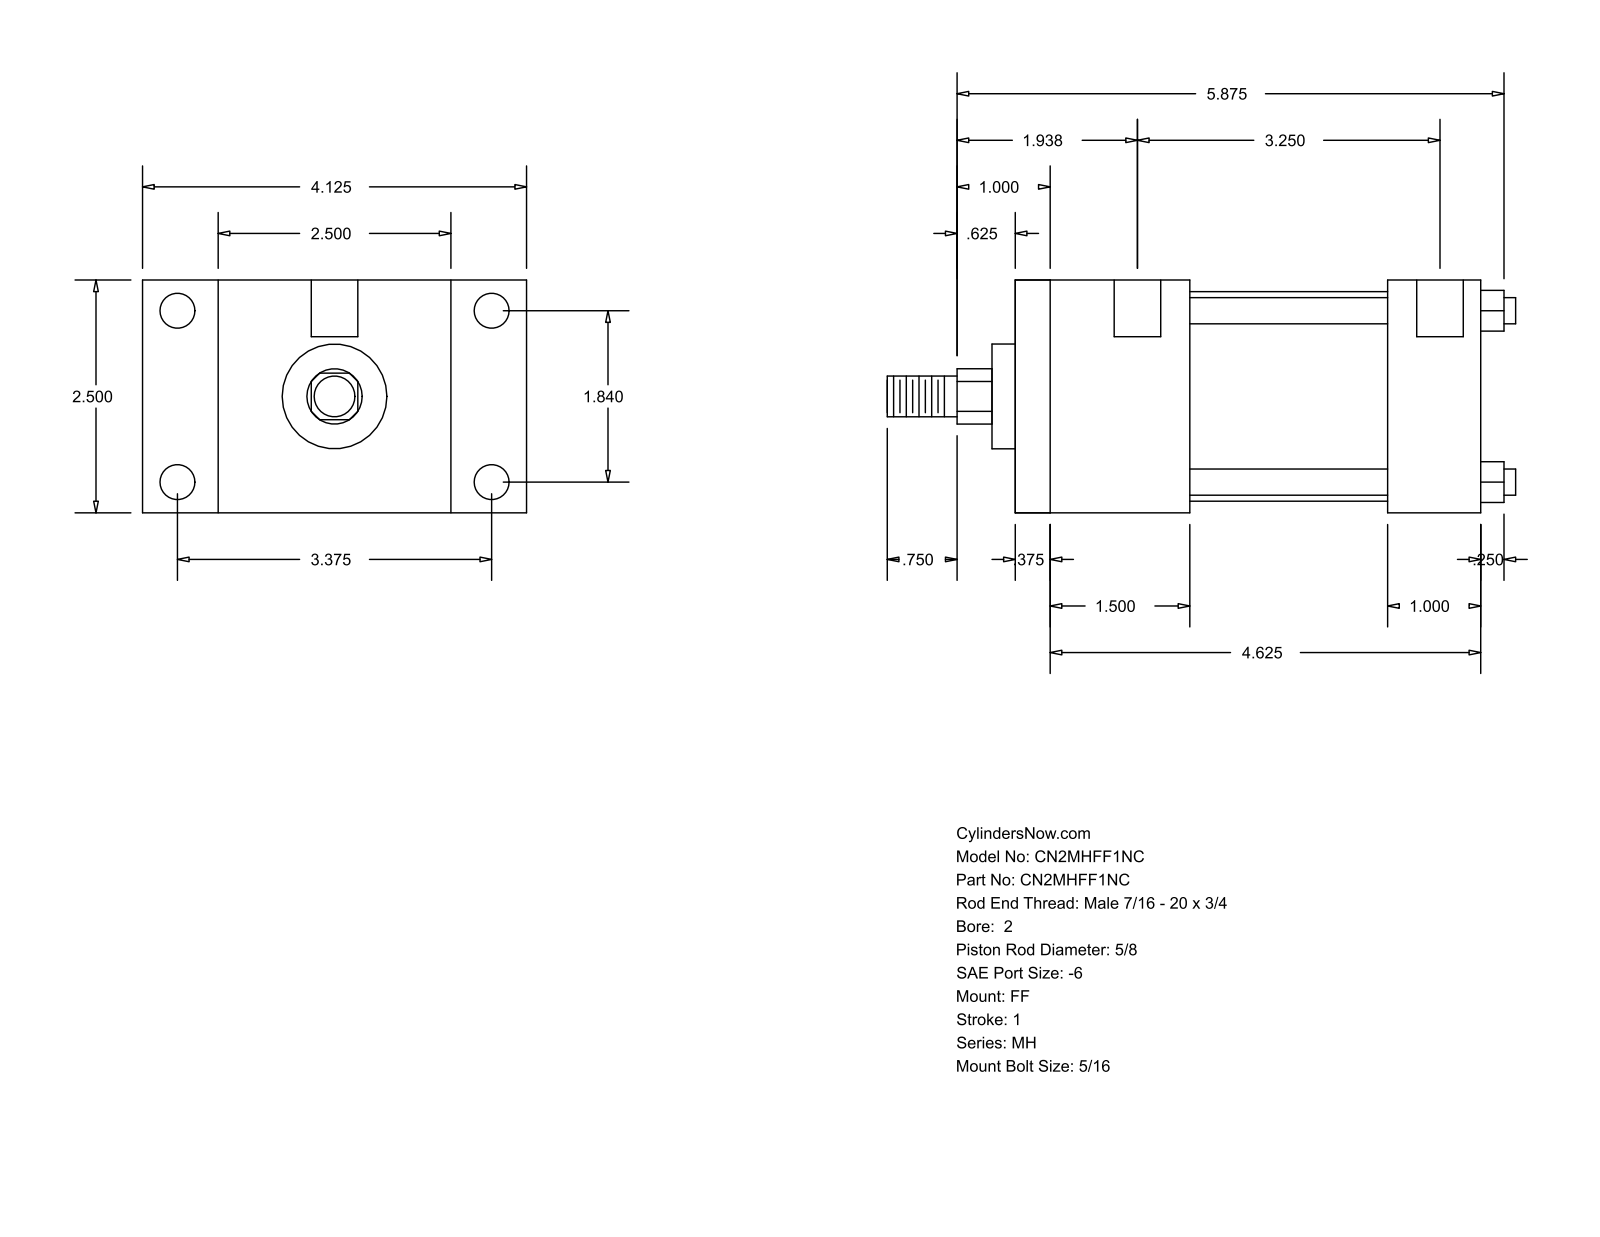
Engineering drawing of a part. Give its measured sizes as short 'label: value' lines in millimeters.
name: MH_FF__0200_0.625
written by: GSSL Pune (CONFIG_CONTROL_DESIGN)
unit: mm
bodies: 0 solids, 92 faces (64 planar, 28 cylindrical, 0 other)
size: 171.45 × 104.78 × 63.5
holes: 4× ⌀5.56, 4× ⌀9.53, 2× ⌀12.7
bosses: 4× ⌀7.14, 1× ⌀57.15, 1× ⌀28.57, 1× ⌀15.88, 1× ⌀11.11
rounds: 1× R7.54
face distances: 63.5, 127, 9.52, 117.48, 53.97, 38.1, 47.62, 101.59, 92.07, 79.38
hole spacings: 46.74, 85.72, 90.49, 97.63, 3.18, 4.76, 82.55, 85.73
